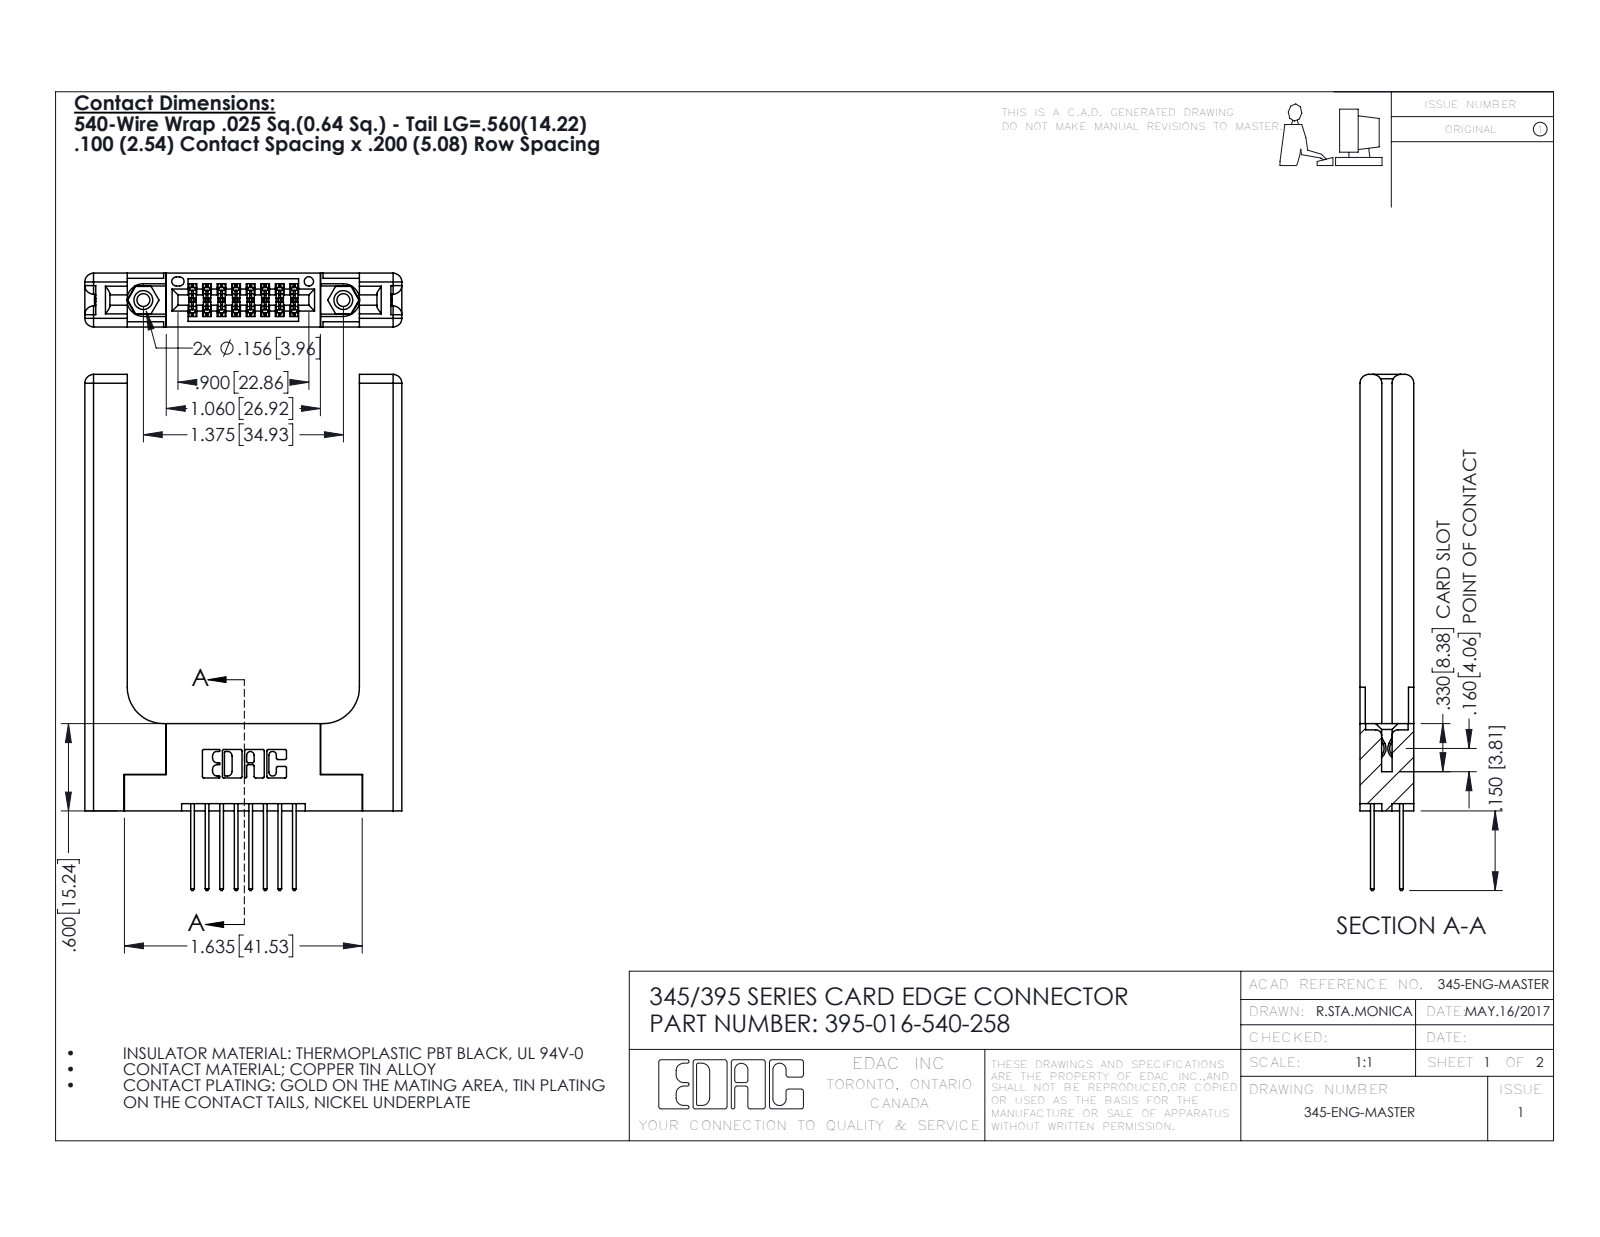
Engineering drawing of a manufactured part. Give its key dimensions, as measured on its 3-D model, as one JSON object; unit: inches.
{"part_name": "345 Part_Flush Mounting Lugs - 0.156 Dia-TH; 345-250-001_345-250-001-102; 395-016-540-258; 345-220-058_345-220-058 (+1 more)", "step_written_by": "SolidWorks 2016 (CONFIG_CONTROL_DESIGN)", "units": "inches", "bodies": {"solids": 21, "faces": 1182, "planar": 756, "cylindrical": 366, "other": 60}, "overall_size": [3.547, 2.179, 0.37], "volume_in3": 0.83, "surface_area_in2": 18.99, "round_holes": [[0.089, 2], [0.125, 2], [0.156, 2], [0.064, 1]], "round_bosses_or_shafts": [[0.155, 2]], "partial_cylinders_radius": [[0.006, 24], [0.01, 22], [0.01, 16], [0.06, 16], [0.007, 6], [0.031, 6], [0.026, 3], [0.014, 2]], "face_to_face_distances": [0.37, 0.072, 0.15, 0.077, 0.148, 0.22, 0.298, 0.2, 1.596, 0.225], "hole_center_spacings": [0.27, 1.144, 1.375]}
